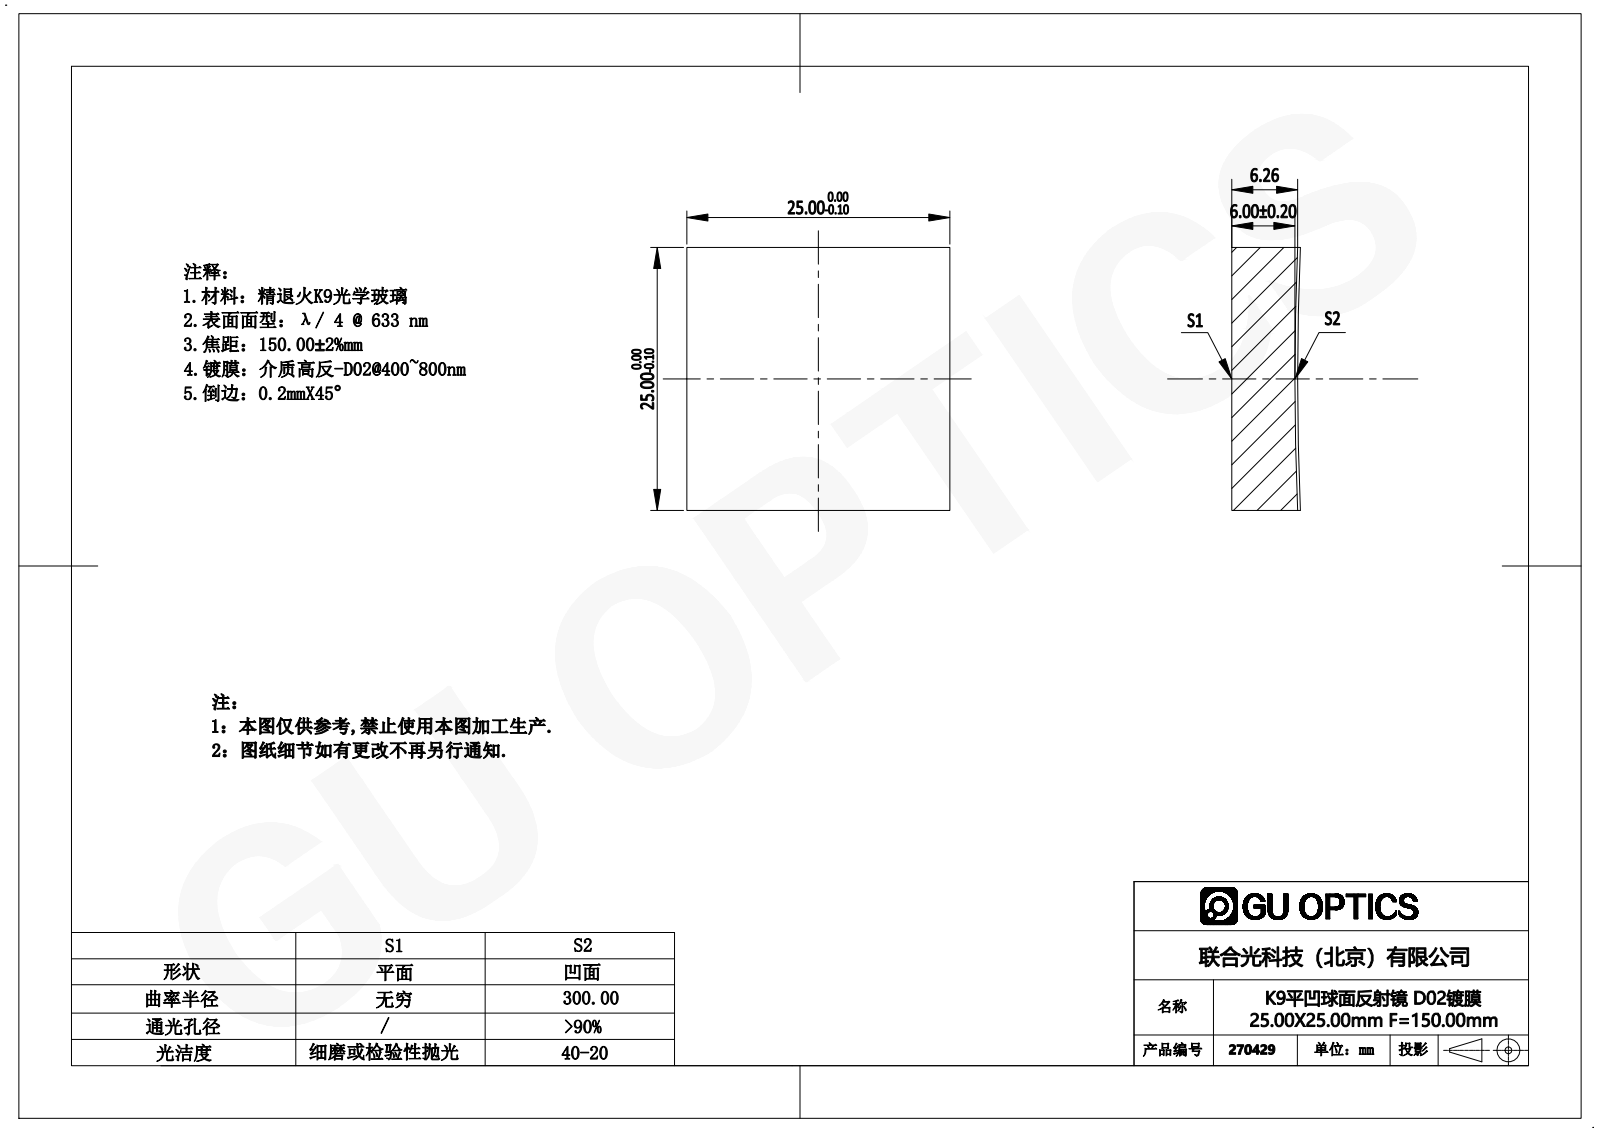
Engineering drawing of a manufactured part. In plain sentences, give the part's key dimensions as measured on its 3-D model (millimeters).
The part is named "270039". Its 3-D file was written by "SolidWorks 2019 (AUTOMOTIVE_DESIGN)". It is 1 solid with 7 faces: 5 planar, 0 cylindrical and 2 other. Overall it measures 25 by 25 by 6.52 millimeters. Its volume is 3 859 cubic millimeters and its surface area 1 885 square millimeters. The main face-to-face distances are 25.
